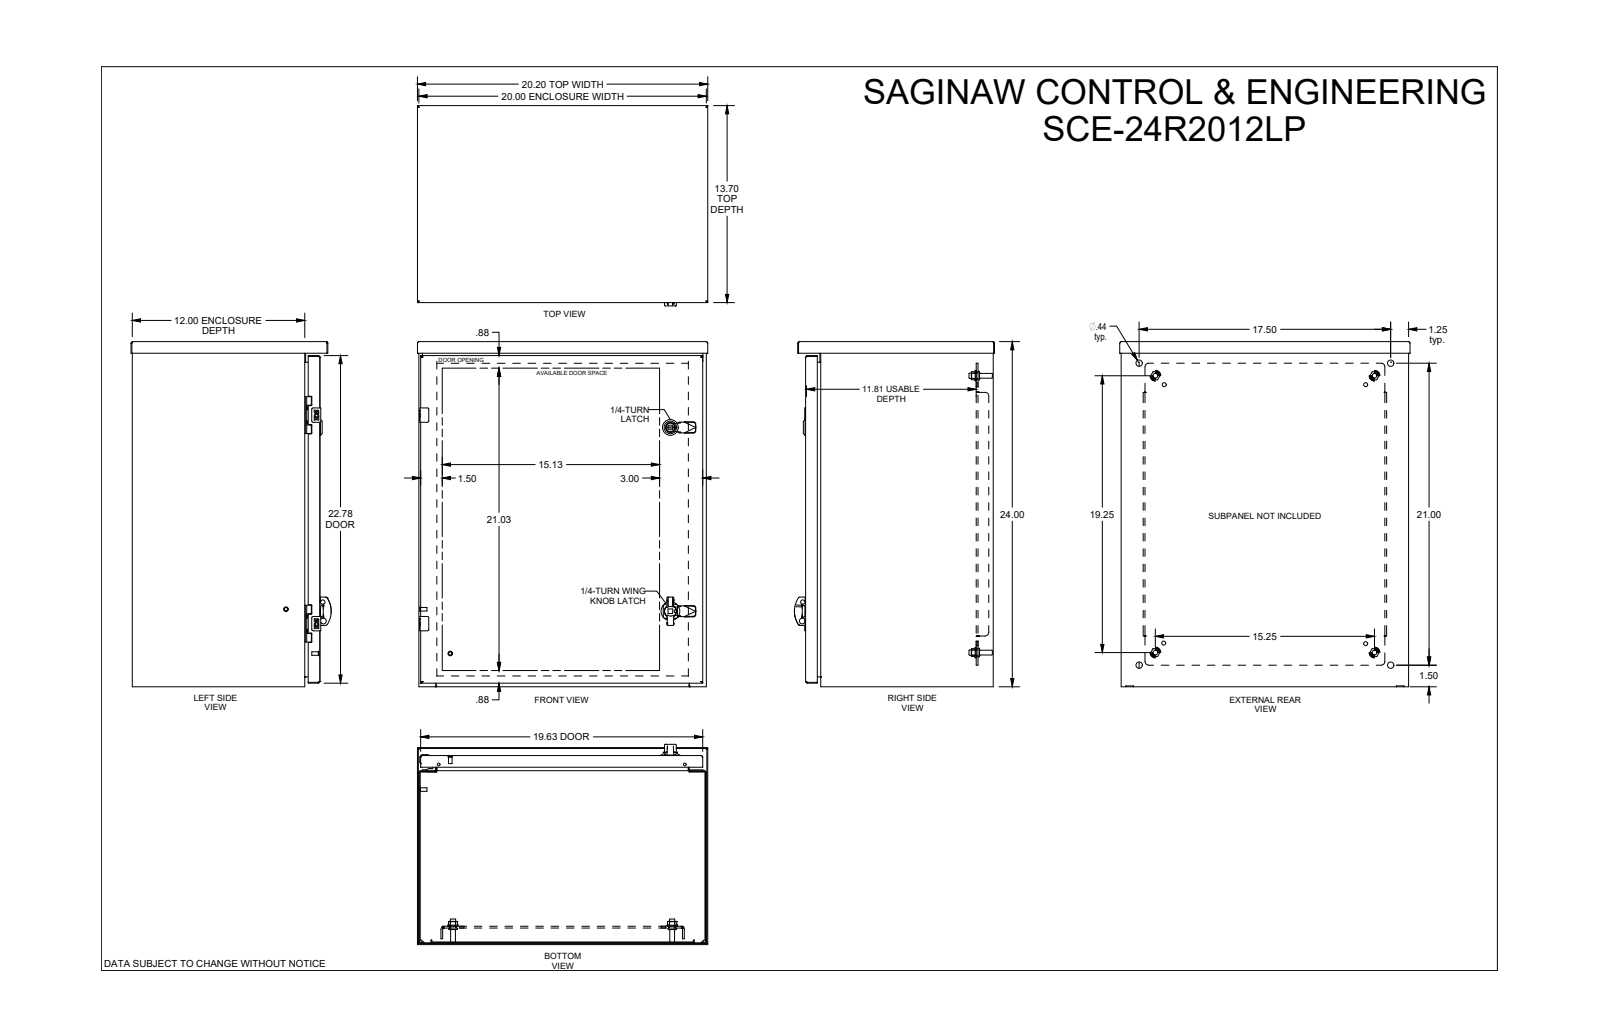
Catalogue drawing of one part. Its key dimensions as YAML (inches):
part_name: "SCE-24R2012LP"
step_written_by: "SolidWorks 2019 (CONFIG_CONTROL_DESIGN)"
units: inches
bodies: {solids: 0, faces: 2365, planar: 1132, cylindrical: 799, other: 434}
overall_size: [24, 20.2, 13.927]
round_holes:
  - {diameter: 0.172, count: 4}
  - {diameter: 0.205, count: 4}
  - {diameter: 0.244, count: 4}
  - {diameter: 0.266, count: 4}
  - {diameter: 0.281, count: 4}
  - {diameter: 0.367, count: 4}
  - {diameter: 0.375, count: 4}
  - {diameter: 0.438, count: 4}
  - {diameter: 0.5, count: 4}
  - {diameter: 0.04, count: 2}
  - {diameter: 0.156, count: 2}
  - {diameter: 0.188, count: 2}
round_bosses_or_shafts:
  - {diameter: 0.17, count: 6}
  - {diameter: 0.366, count: 4}
  - {diameter: 0.332, count: 4}
  - {diameter: 0.25, count: 4}
  - {diameter: 0.24, count: 4}
  - {diameter: 0.196, count: 3}
  - {diameter: 0.866, count: 2}
  - {diameter: 0.802, count: 2}
partial_cylinders:
  - {radius: 0.015, count: 72}
  - {radius: 0.012, count: 60}
  - {radius: 0.01, count: 26}
  - {radius: 0.02, count: 24}
  - {radius: 0.112, count: 21}
  - {radius: 0.052, count: 19}
  - {radius: 0.03, count: 15}
  - {radius: 0.031, count: 12}
face_to_face_distances: [0.06, 19.94, 0.06, 12.933, 12.993, 23.94, 13.053, 12.993, 0.125, 1]
hole_center_spacings: [14.5, 0.024, 0.493, 0.985, 16.398, 0.875, 2.296, 14.644]
